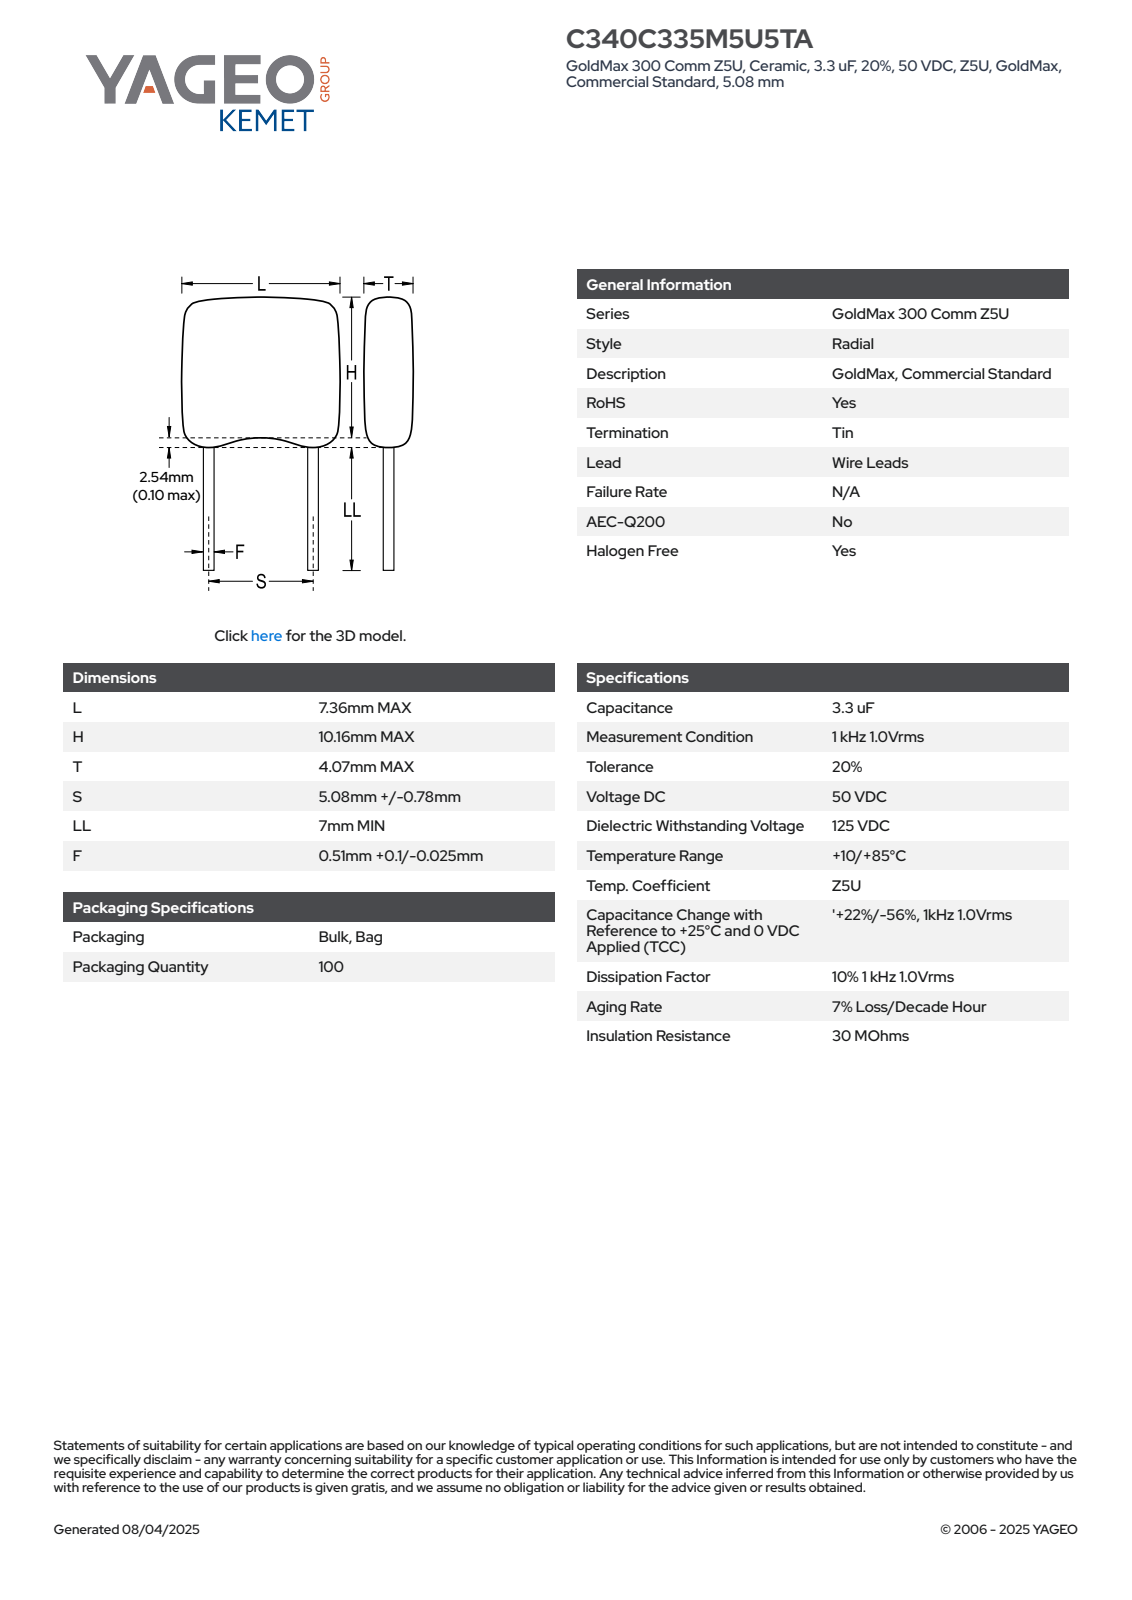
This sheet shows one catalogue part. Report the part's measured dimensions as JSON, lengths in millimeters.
{"part_name": "CCR_KRCST2_C340_L7.36H10.16T4.07S5.08LL7F0.61", "step_written_by": "SolidWorks 2014 (AUTOMOTIVE_DESIGN)", "units": "millimeters", "bodies": {"solids": 4, "faces": 94, "planar": 66, "cylindrical": 16, "other": 12}, "overall_size": [19.7, 7.36, 4.08], "volume_mm3": 340, "surface_area_mm2": 341, "round_bosses_or_shafts": [[0.61, 2]], "partial_cylinders_radius": [[1, 10]], "face_to_face_distances": [4.07, 7.36, 4.08, 12.7, 7, 19.7, 1.01, 13.86, 6.86, 5.84]}
